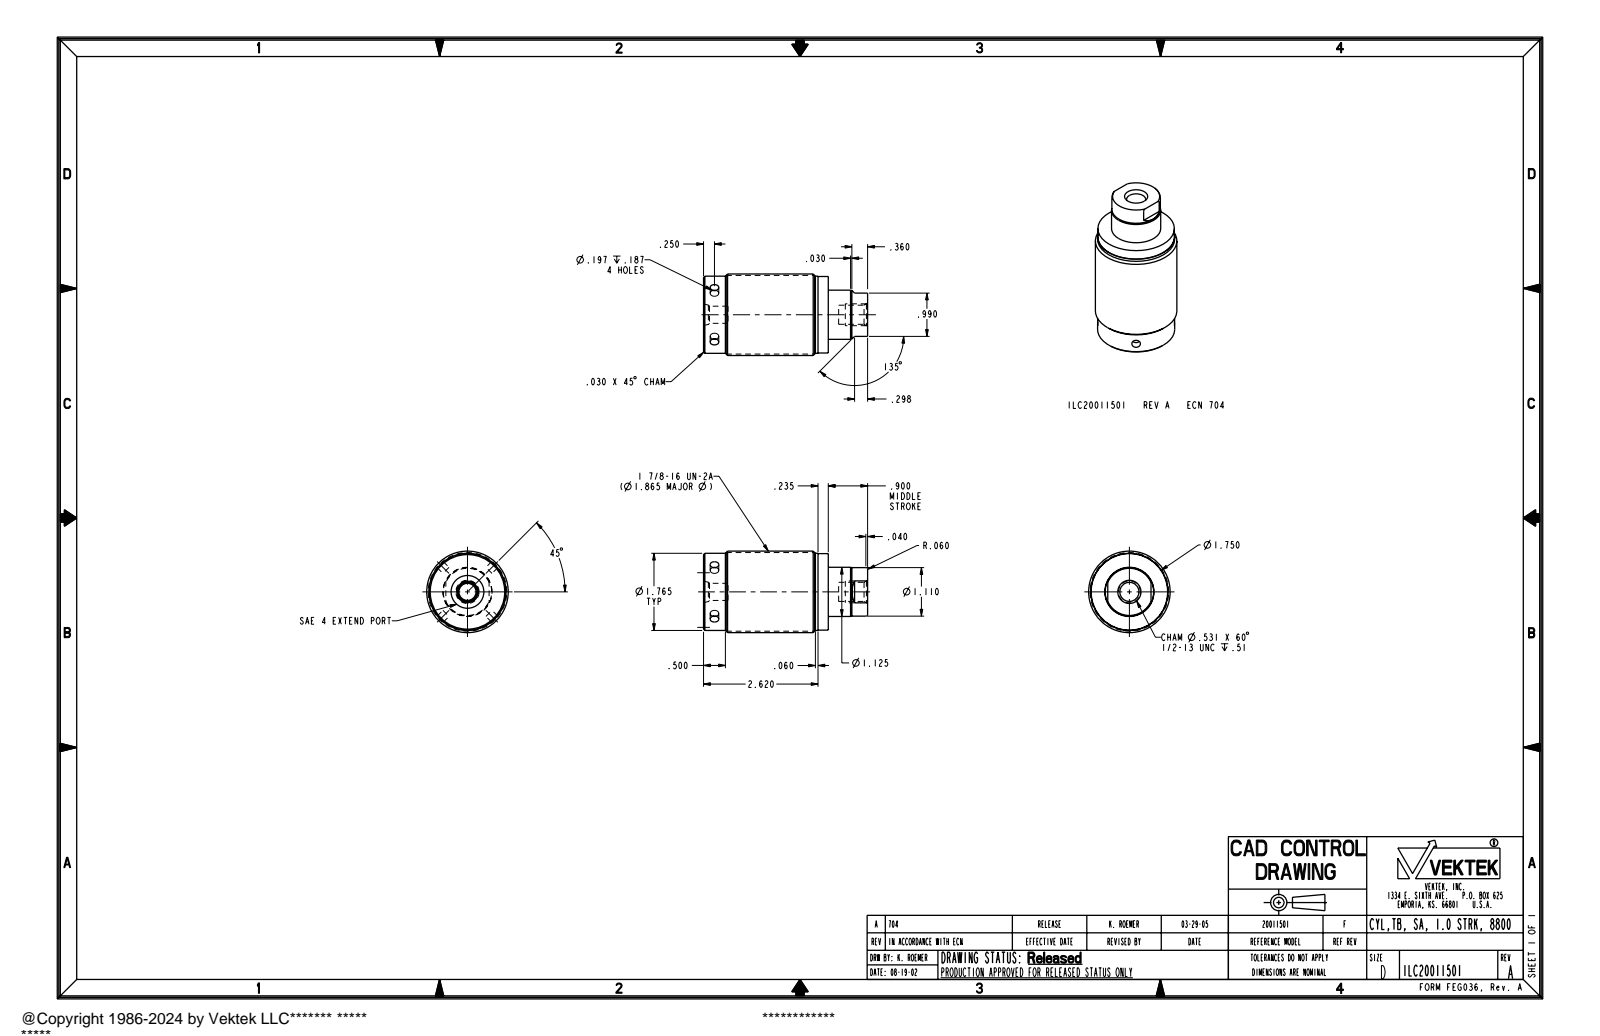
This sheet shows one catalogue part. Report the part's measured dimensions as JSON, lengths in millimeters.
{"part_name": "ILC20011501", "step_written_by": "PRO/ENGINEER BY PARAMETRIC TECHNOLOGY CORPORATION, 2004290 (AUTOMOTIVE_DESIGN_CC2)", "units": "millimeters", "bodies": {"solids": 1, "faces": 62, "planar": 16, "cylindrical": 30, "other": 16}, "overall_size": [95.4, 47.4, 47.4], "volume_mm3": 134600, "surface_area_mm2": 25050, "round_holes": [[5, 2], [10, 1], [11.1, 1], [19.1, 1]], "round_bosses_or_shafts": [[47.4, 1], [45.7, 1], [44.8, 1], [44.5, 1], [28.6, 1], [28.2, 1], [12.7, 1]], "face_to_face_distances": [72.5, 22.9, 95.4, 95.1, 72.3, 16.8, 6, 78.3, 78.5, 25.1]}
